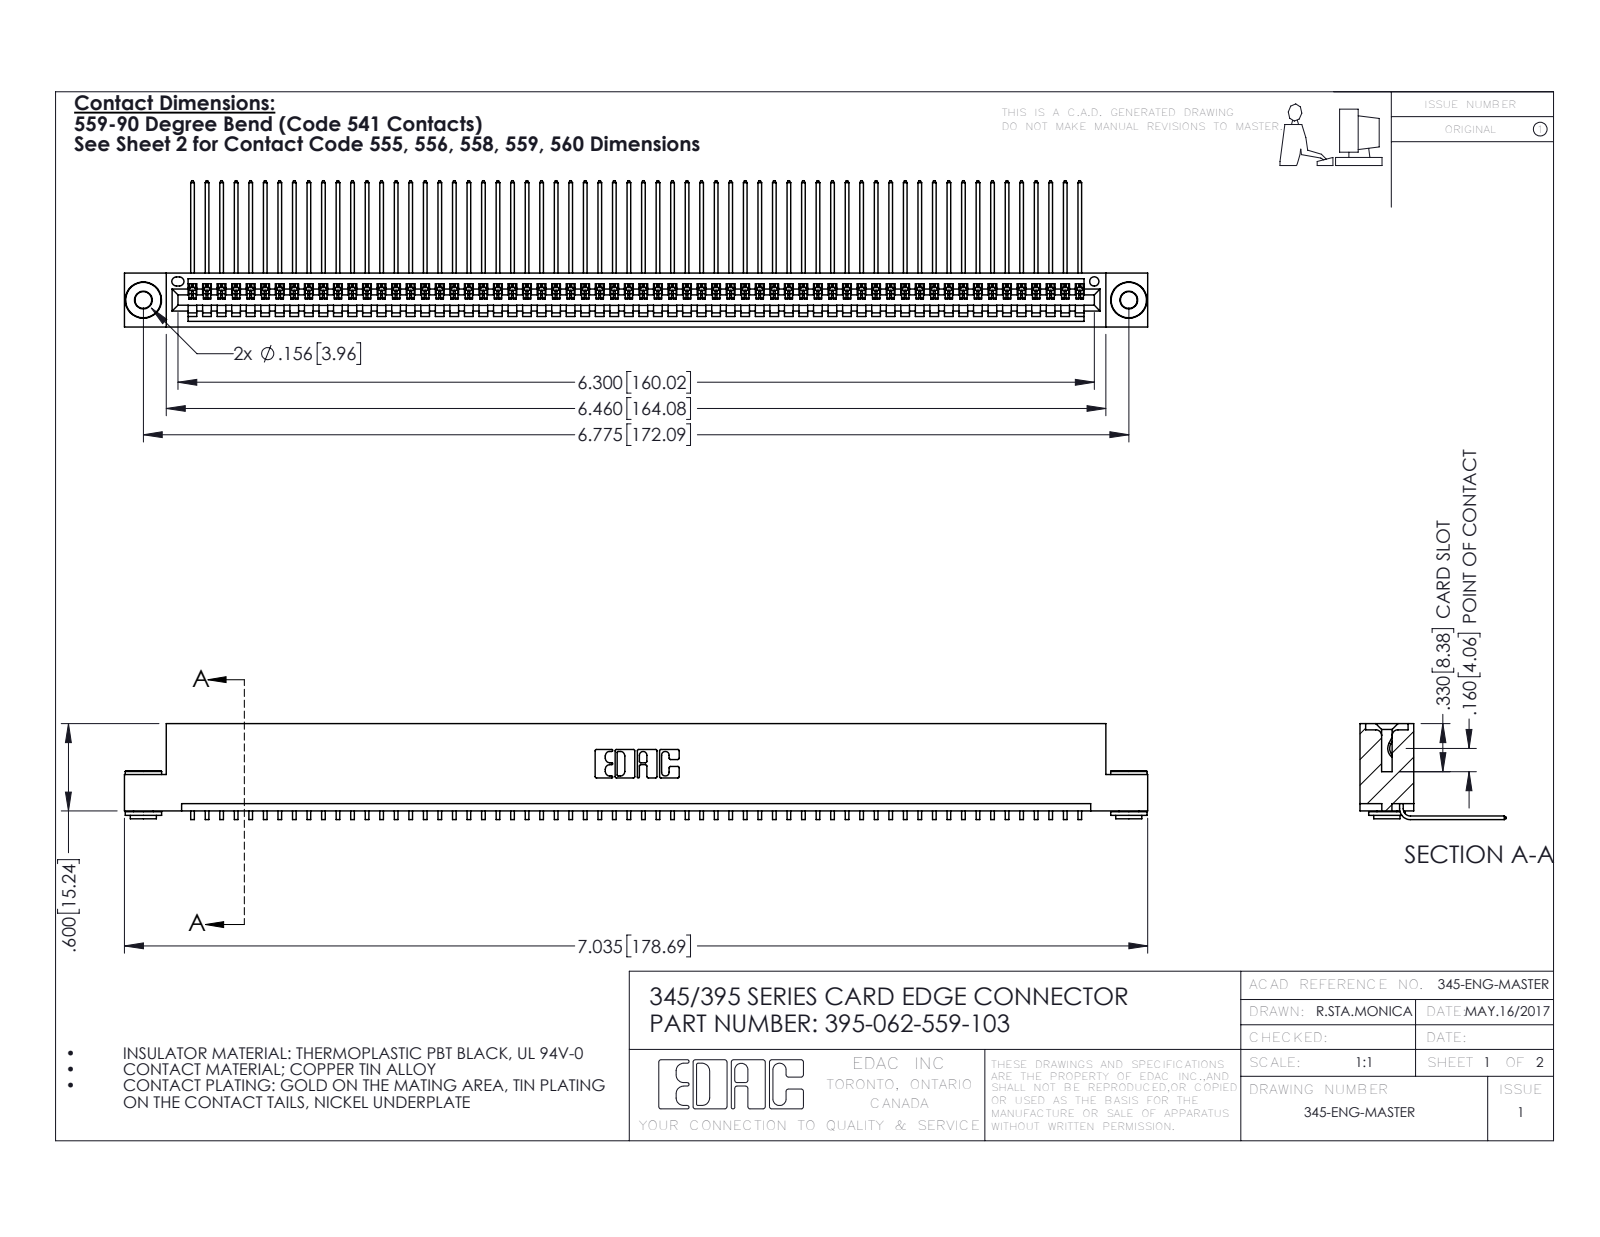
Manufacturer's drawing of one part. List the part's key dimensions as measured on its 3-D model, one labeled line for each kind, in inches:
Part name (STEP PRODUCT): 395-062-559-103; 345-250-002_345-250-002-102; 345 Part_Flush Mounting Lugs - 0.156 Dia-TH; 345-292-001_558 559 Tail - 1
STEP written by: SolidWorks 2016 (CONFIG_CONTROL_DESIGN)
Units: inches
Bodies: 65 solids, 3884 faces (2694 planar, 1182 cylindrical, 8 other)
Overall size (bounding box): 7.035 × 1.005 × 0.659
Volume: 1.059 in³ · Surface area: 38.4 in²
Round holes (diameter × count): ⌀0.116 ×2, ⌀0.156 ×2, ⌀0.064 ×1
Round bosses / shafts (diameter × count): ⌀0.25 ×2, ⌀0.18 ×2, ⌀0.136 ×2
Partial cylindrical surfaces — rounded edges, fillets, slot ends (radius × count): R0.006 ×124, R0.01 ×22, R0.007 ×6, R0.031 ×6, R0.026 ×3, R0.031 ×2, R0.04 ×2, R0.014 ×1
Main face-to-face distances: 0.072, 0.298, 0.37, 0.2, 0.025, 0.098, 0.272, 0.225, 0.149, 0.072
Hole centre spacings: 0.27, 6.539, 6.775
